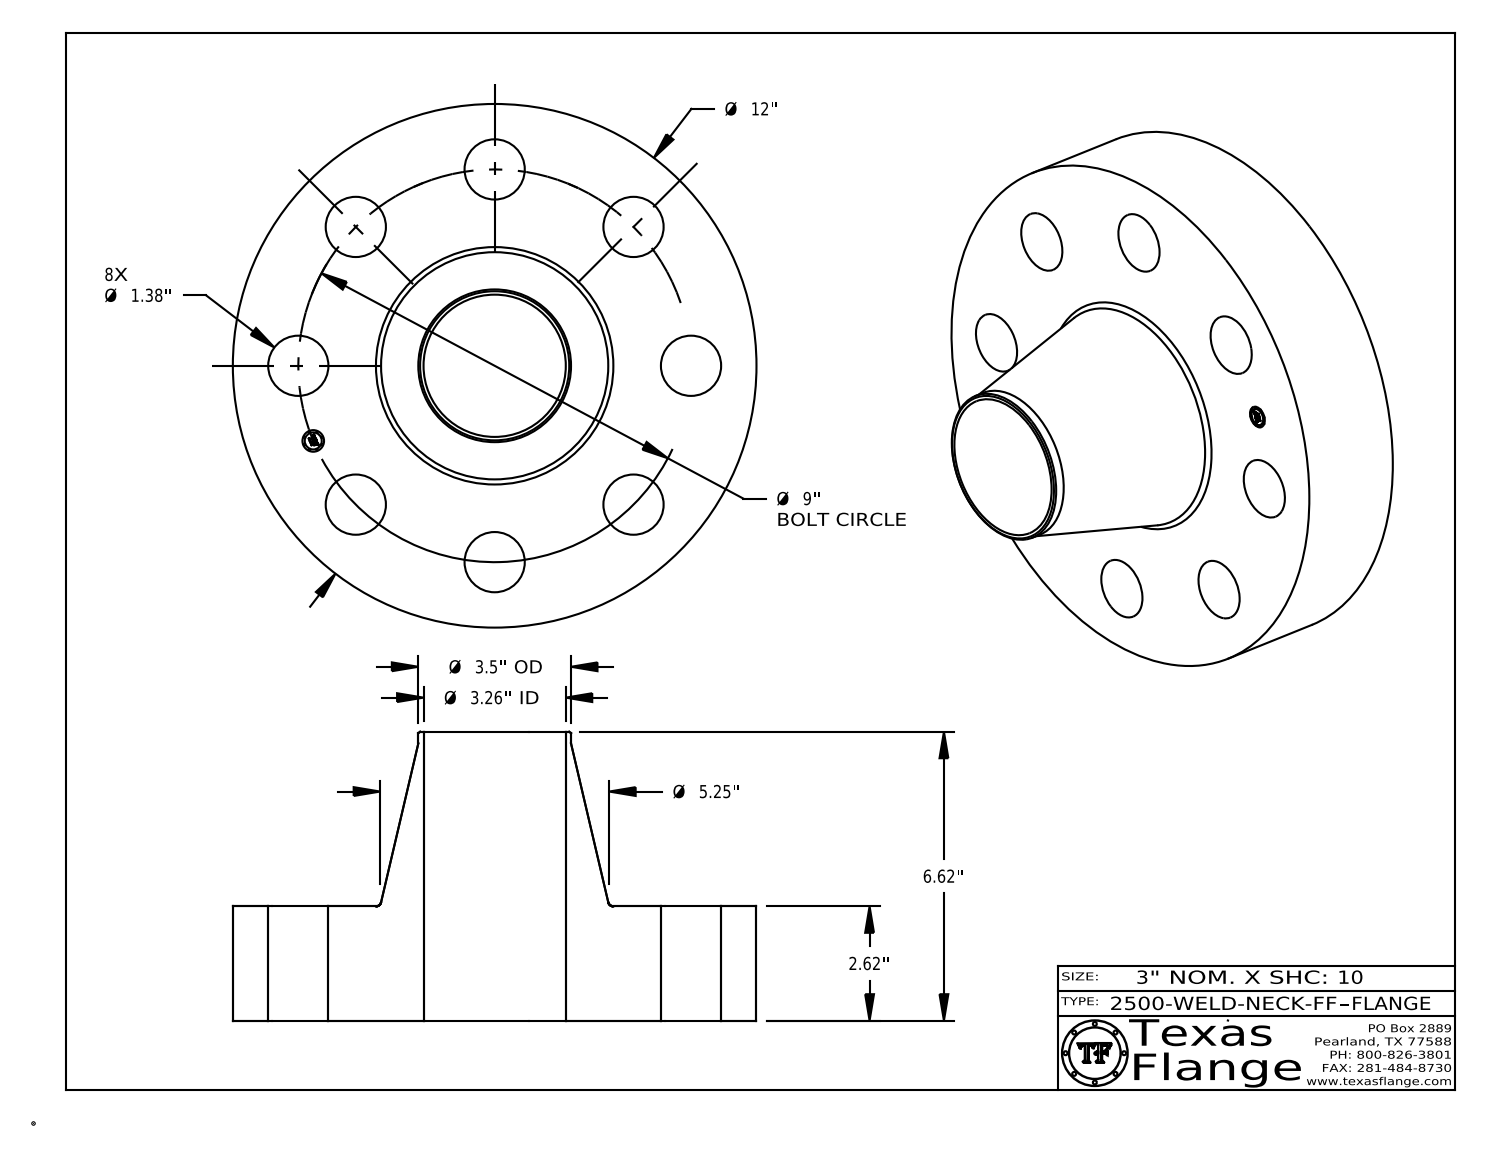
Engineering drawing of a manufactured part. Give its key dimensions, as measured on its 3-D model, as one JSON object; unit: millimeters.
{"part_name": "2500-WELD-NECK-FF", "step_written_by": "CATIA V5 STEP AP214 (AUTOMOTIVE_DESIGN)", "units": "millimeters", "bodies": {"solids": 1, "faces": 416, "planar": 368, "cylindrical": 42, "other": 6}, "overall_size": [304.8, 304.8, 168.1], "volume_mm3": 4411000, "surface_area_mm2": 313500, "round_holes": [[35.1, 8], [12.6, 1], [82.8, 1]], "round_bosses_or_shafts": [[0.8, 8], [304.8, 1], [88.9, 1], [9.9, 1]], "face_to_face_distances": [66.5, 168.1, 101.6, 66.2, 0.4, 102, 3.8, 3.7, 0.7, 2.4], "hole_center_spacings": [114.3, 87.5, 161.6, 211.2, 44.6, 127, 190.1, 228.6]}
